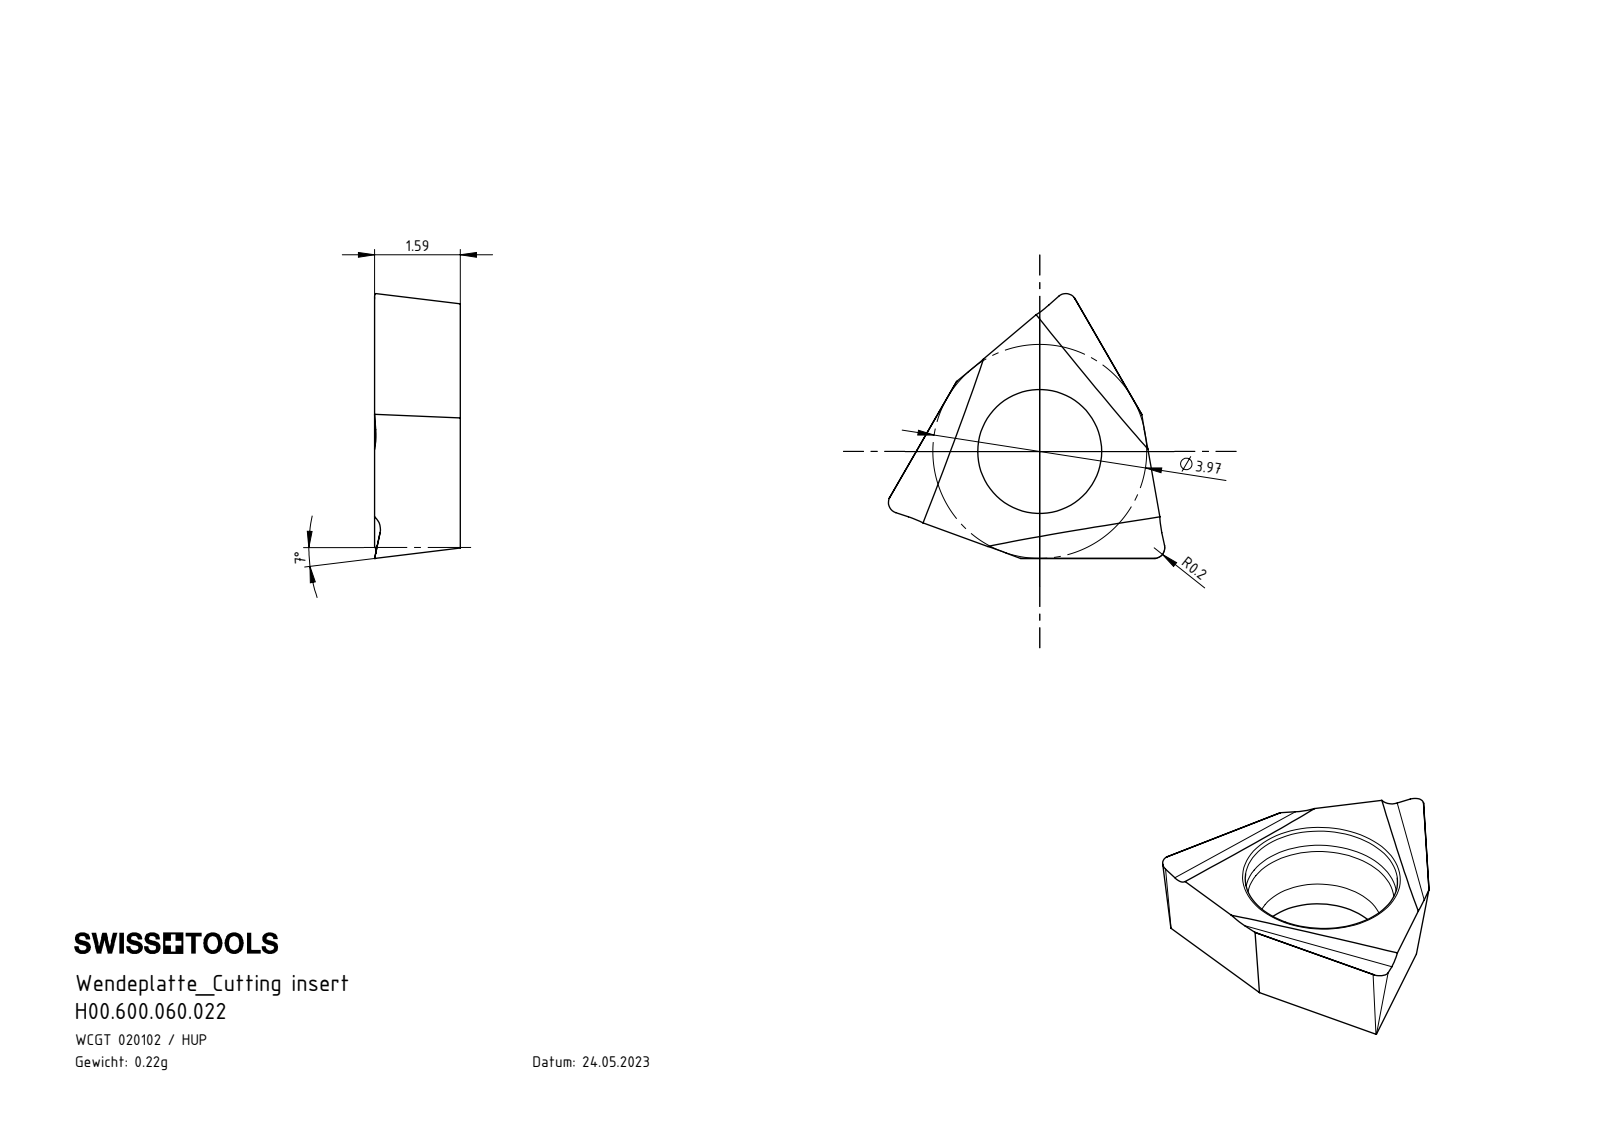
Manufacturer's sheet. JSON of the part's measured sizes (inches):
{"part_name": "H00.600.060.022", "step_written_by": "SolidWorks 2022 (AUTOMOTIVE_DESIGN)", "units": "inches", "bodies": {"solids": 1, "faces": 31, "planar": 14, "cylindrical": 5, "other": 12}, "overall_size": [0.202, 0.194, 0.063], "volume_in3": 0.001, "surface_area_in2": 0.087, "round_holes": [[0.091, 1]], "partial_cylinders_radius": [[0.012, 3]], "face_to_face_distances": [0.063]}
